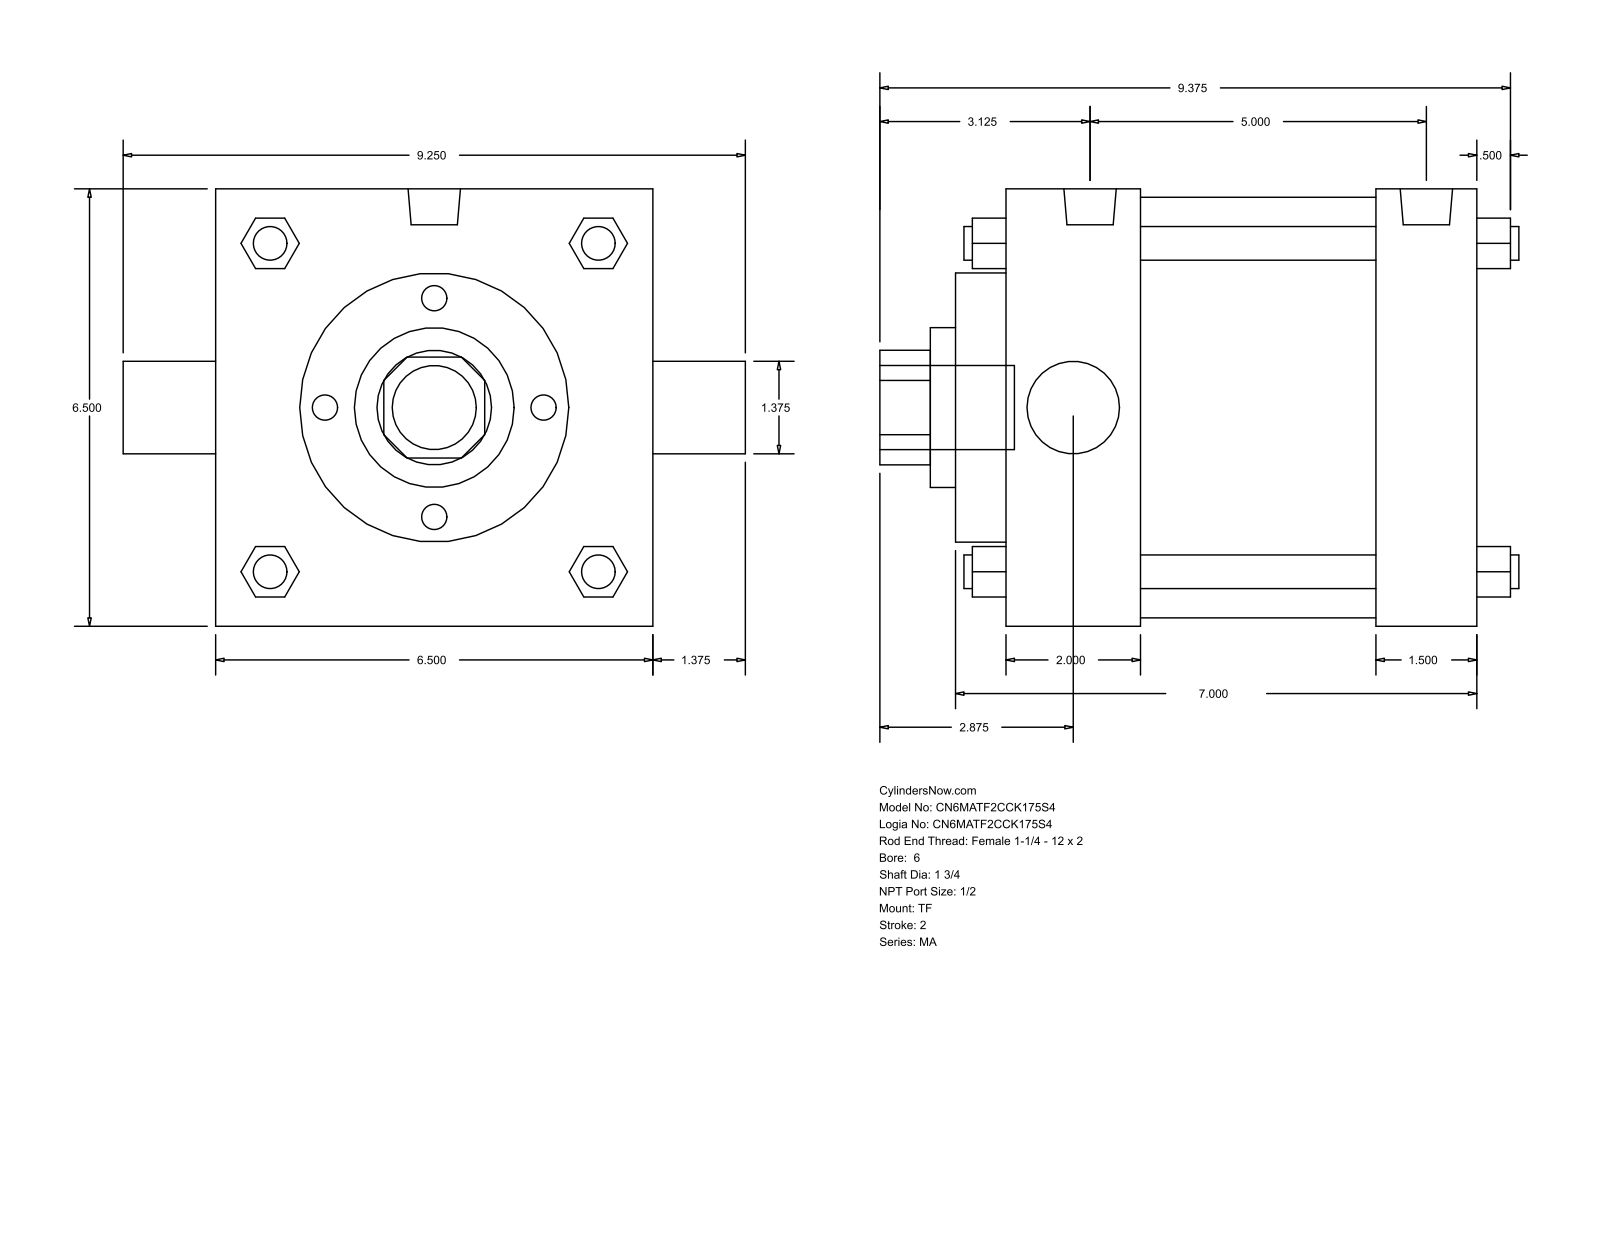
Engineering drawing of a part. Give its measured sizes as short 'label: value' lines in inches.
name: MA_TF__0600_1.75
written by: GSSL Pune (CONFIG_CONTROL_DESIGN)
unit: in
bodies: 0 solids, 122 faces (93 planar, 29 cylindrical, 0 other)
size: 9.5 × 9.25 × 6.5
holes: 1× ⌀1.375, 1× ⌀1.75, 1× ⌀2.375, 1× ⌀4, 1× ⌀6.25
bosses: 4× ⌀0.5, 3× ⌀0.687, 2× ⌀0.778, 1× ⌀1.25
rounds: 1× R0.852
face distances: 6.5, 7, 0.75, 2, 5.5, 5, 3.5, 1.5, 2.75, 6.25
